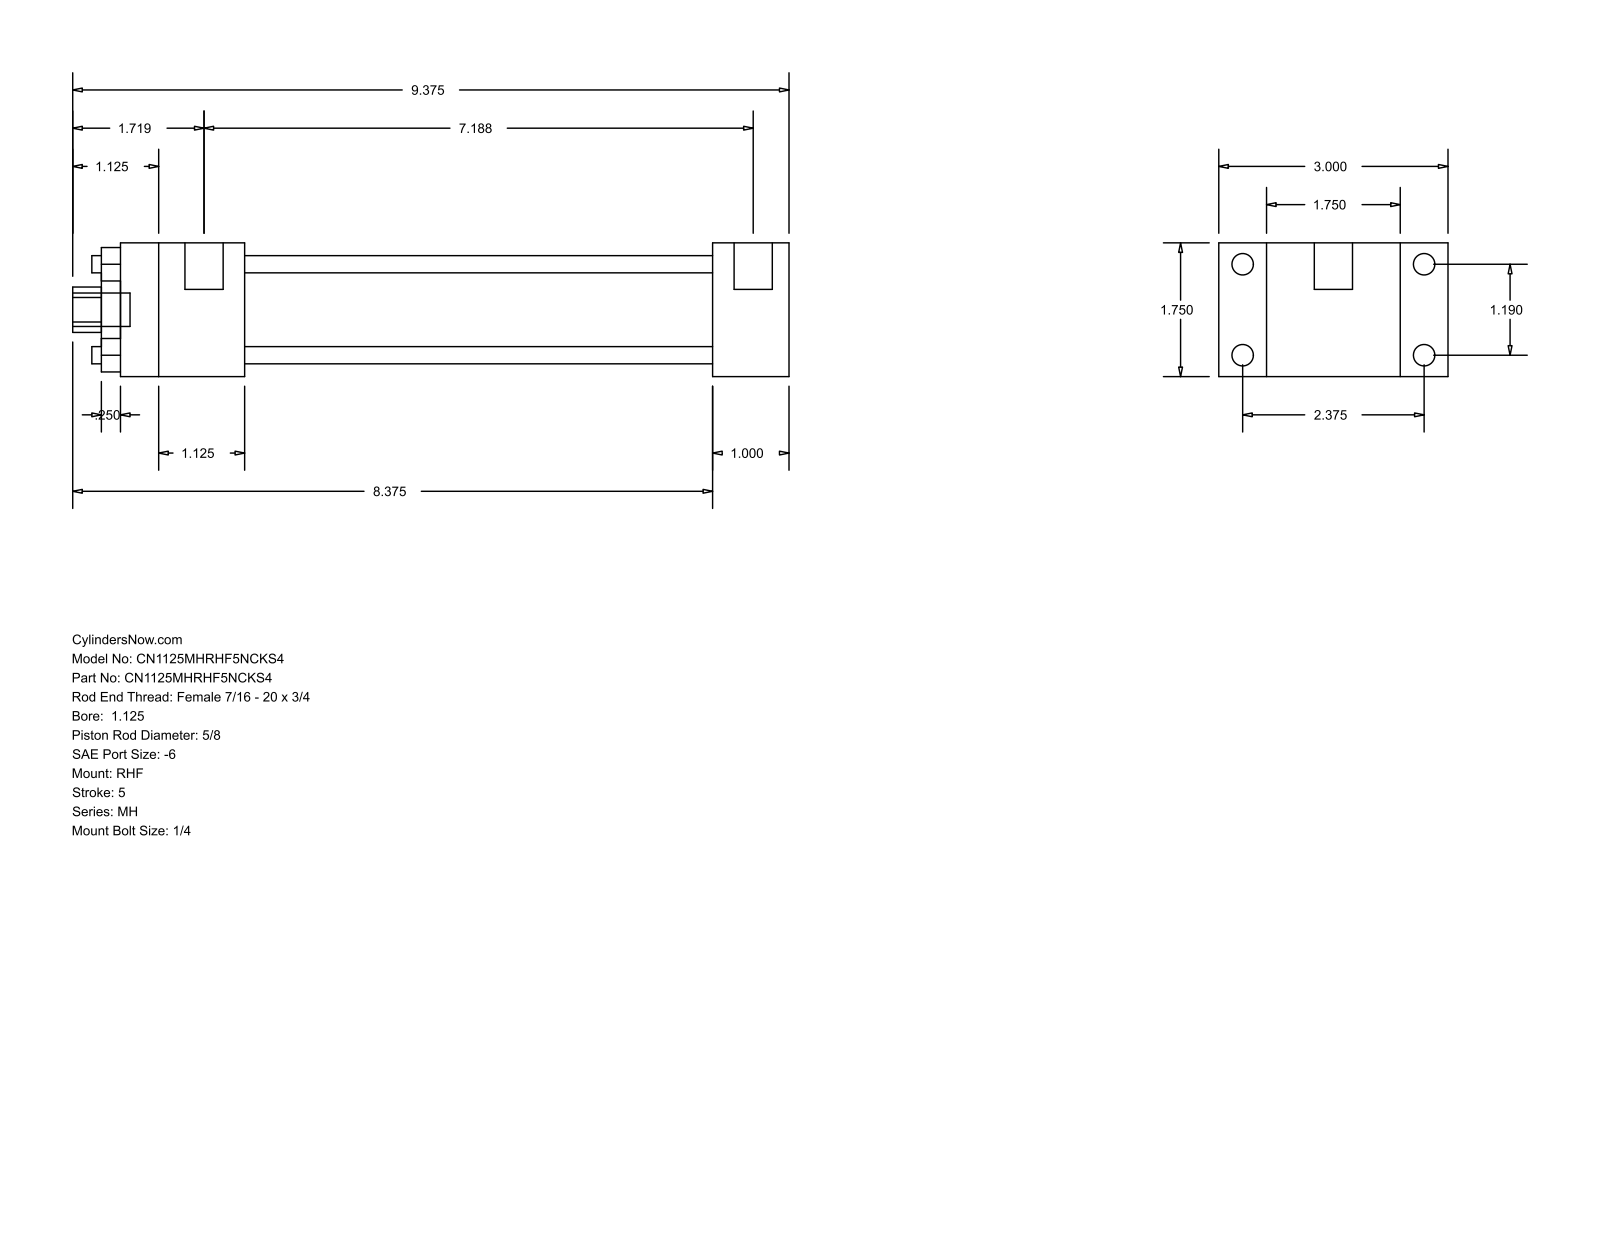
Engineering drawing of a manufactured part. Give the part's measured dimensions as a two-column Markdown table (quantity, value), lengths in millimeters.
| quantity | value |
| --- | --- |
| part name | MH_RHF__0112_0.625 |
| STEP written by | GSSL Pune (CONFIG_CONTROL_DESIGN) |
| units | millimeters |
| bodies | 0 solids, 88 faces (60 planar, 28 cylindrical, 0 other) |
| overall size | 238.12 × 76.2 × 44.45 |
| round holes (diameter × count) | 5.71 × 4, 15.88 × 1, 28.57 × 1, 34.92 × 1 |
| round bosses / shafts (diameter × count) | 7.14 × 4, 5.56 × 4, 12.7 × 2, 11.11 × 1 |
| partial cylindrical surfaces (radius × count) | 7.54 × 1 |
| main face-to-face distances | 44.46, 15.87, 60.33, 25.4, 76.2, 155.57, 180.97, 41.27, 196.84, 222.24 |
| hole center spacings | 21.37, 30.22, 42.74 |
